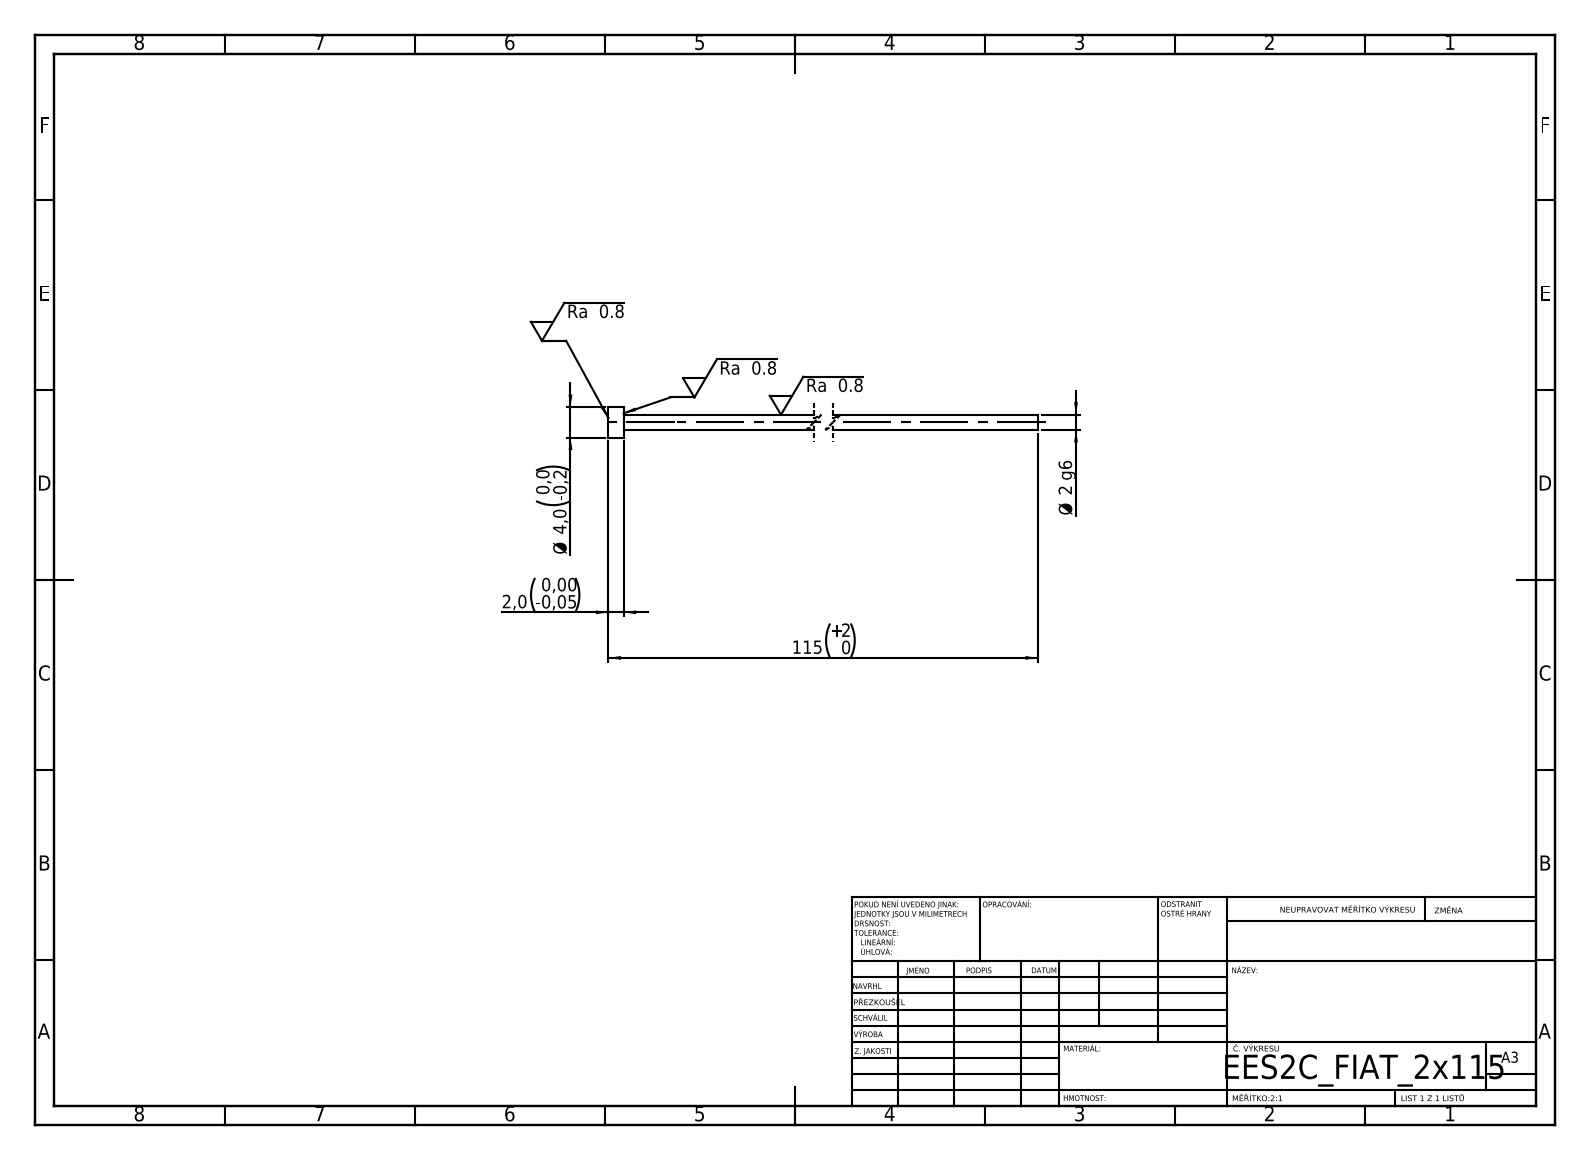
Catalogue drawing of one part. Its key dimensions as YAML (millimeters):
step_written_by: "SolidWorks 2019 (CONFIG_CONTROL_DESIGN)"
units: millimeters
bodies: {solids: 1, faces: 7, planar: 3, cylindrical: 4, other: 0}
overall_size: [115, 4, 4]
volume: 380
surface_area: 760
round_bosses_or_shafts:
  - {diameter: 4, count: 1}
  - {diameter: 2, count: 1}
face_to_face_distances: [2, 115, 113]
